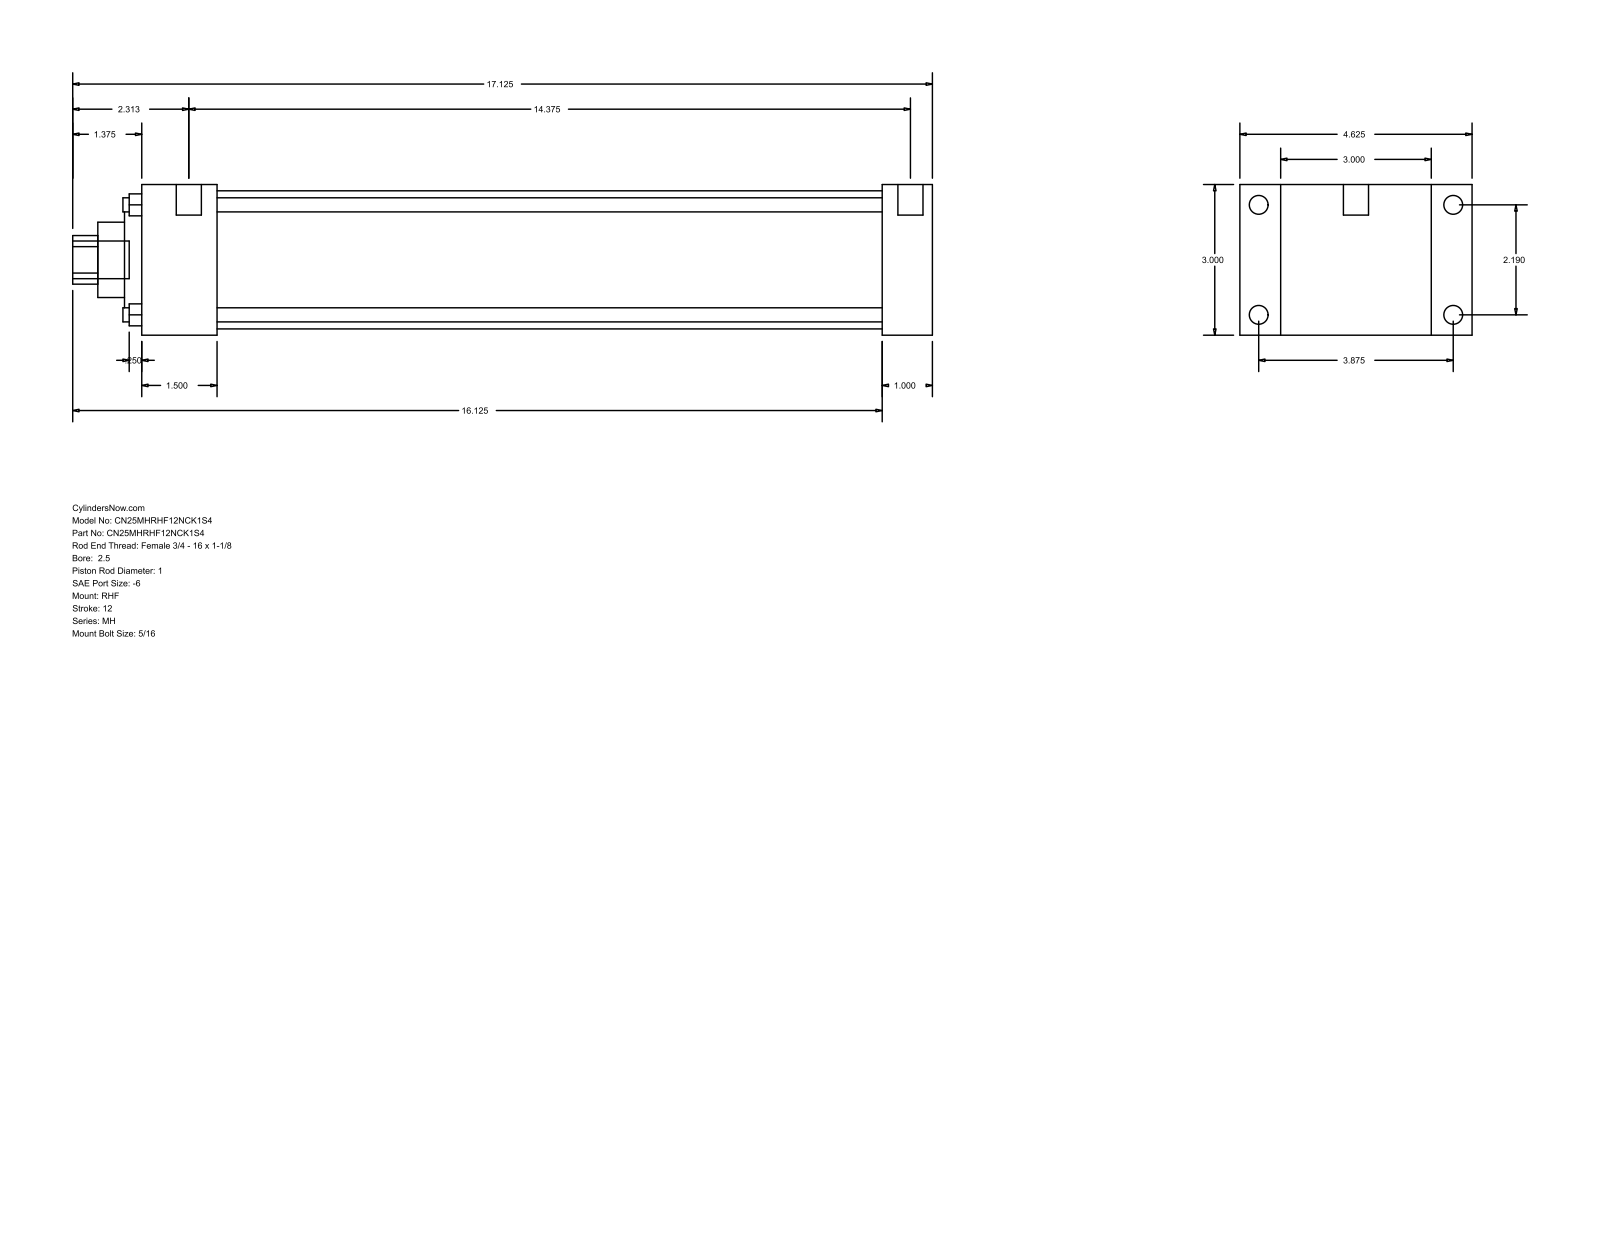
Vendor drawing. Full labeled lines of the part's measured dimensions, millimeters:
Part name (STEP PRODUCT): MH_RHF__0250_1
STEP written by: GSSL Pune (CONFIG_CONTROL_DESIGN)
Units: millimetres
Bodies: 0 solids, 90 faces (61 planar, 29 cylindrical, 0 other)
Overall size (bounding box): 434.98 × 117.47 × 76.2
Round holes (diameter × count): ⌀7.14 ×4, ⌀25.4 ×1, ⌀38.1 ×1, ⌀60.33 ×1, ⌀69.85 ×1
Round bosses / shafts (diameter × count): ⌀9.53 ×4, ⌀5.56 ×4, ⌀12.7 ×2, ⌀19.05 ×1
Partial cylindrical surfaces — rounded edges, fillets, slot ends (radius × count): R12.29 ×1
Main face-to-face distances: 76.2, 25.41, 20.64, 96.84, 374.65, 400.06, 117.48, 38.11, 336.54, 361.95
Hole centre spacings: 39.33, 55.62, 78.66
